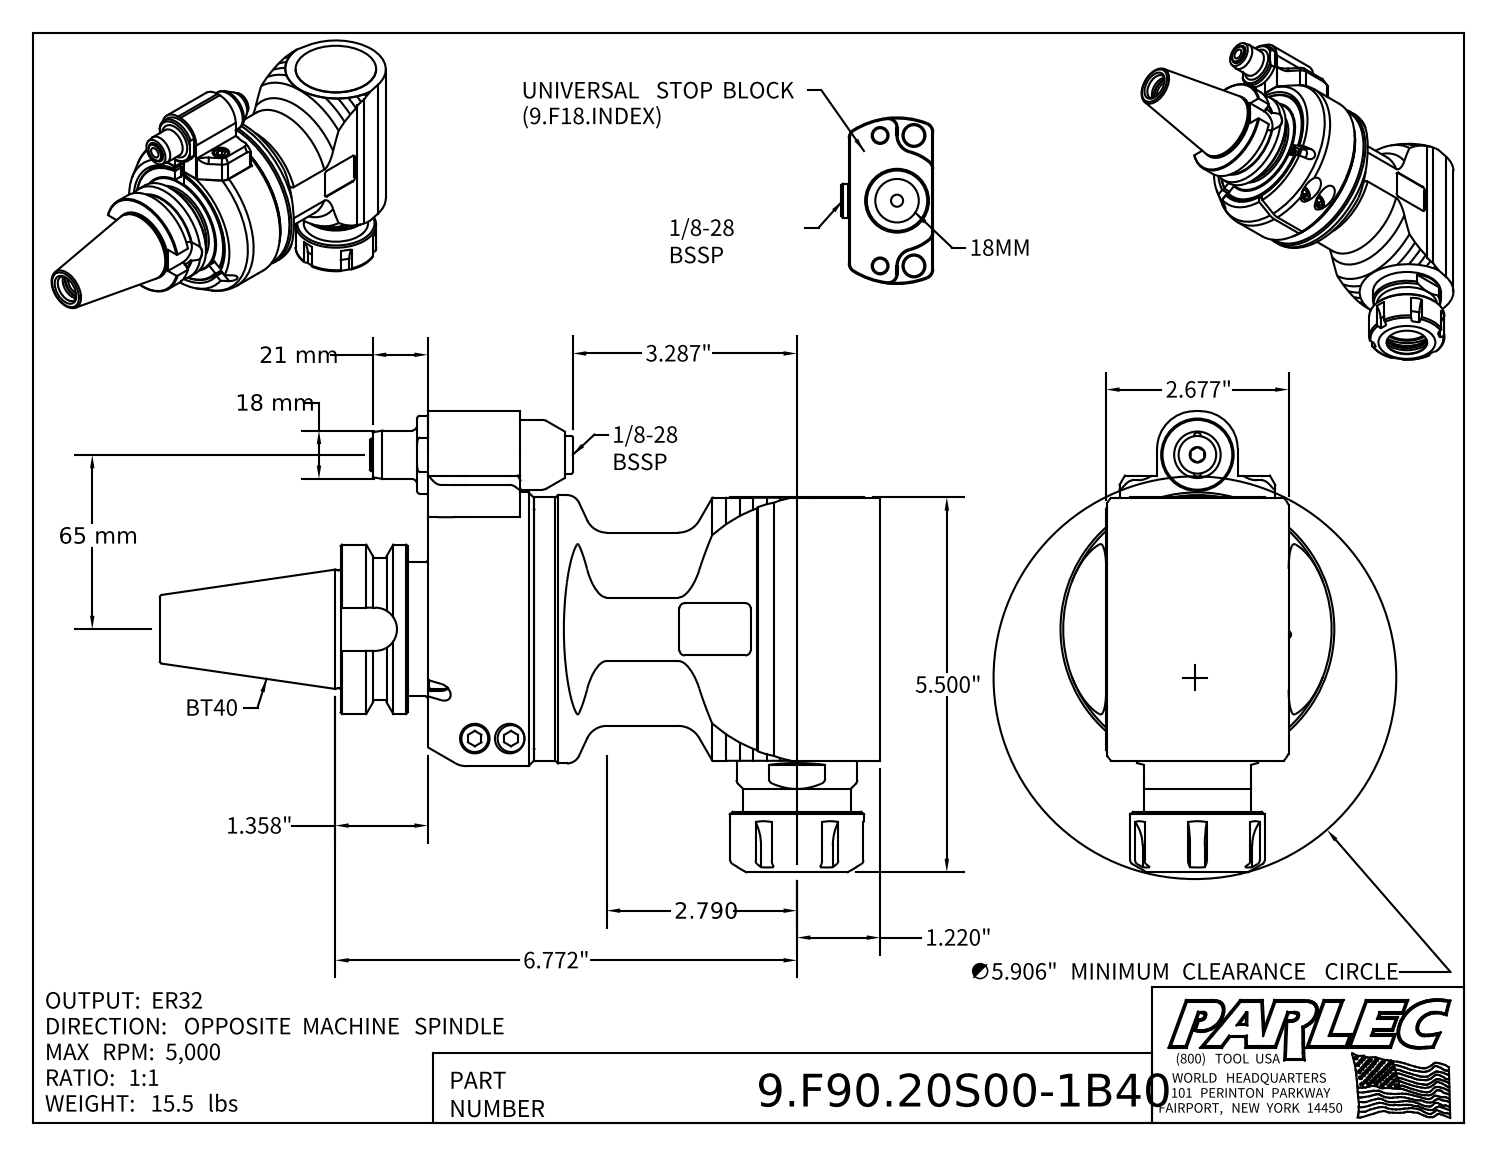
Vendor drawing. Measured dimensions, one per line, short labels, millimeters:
name: 9.F90.20S00-1B40; 9_F90_20S00; 9_GA1_346_2 (Type 1, BT40, 65mm)
written by: Autodesk Inventor 2022 (AUTOMOTIVE_DESIGN)
unit: mm
bodies: 8 solids, 548 faces (256 planar, 121 cylindrical, 171 other)
size: 268.4 × 171.8 × 102
volume: 1 210 000 mm³; area: 167 400 mm²
holes: 2× ⌀2.6, 2× ⌀4.2, 2× ⌀5, 2× ⌀10.4, 2× ⌀11, 2× ⌀12.5, 2× ⌀27, 1× ⌀2.5, 1× ⌀3, 1× ⌀6.5, 1× ⌀7, 1× ⌀12
bosses: 4× ⌀10, 4× ⌀6, 2× ⌀50, 2× ⌀18, 2× ⌀12, 2× ⌀2.5, 1× ⌀102, 1× ⌀100
rounds: 12× R2, 6× R15, 4× R4, 2× R0.5, 2× R1, 2× R3.5, 2× R5, 2× R14
face distances: 32, 0.5, 32.5, 39.5, 7.5, 7.2, 7, 8, 5, 68
hole spacings: 7, 13, 14, 43.7, 58, 65, 72, 105.1
